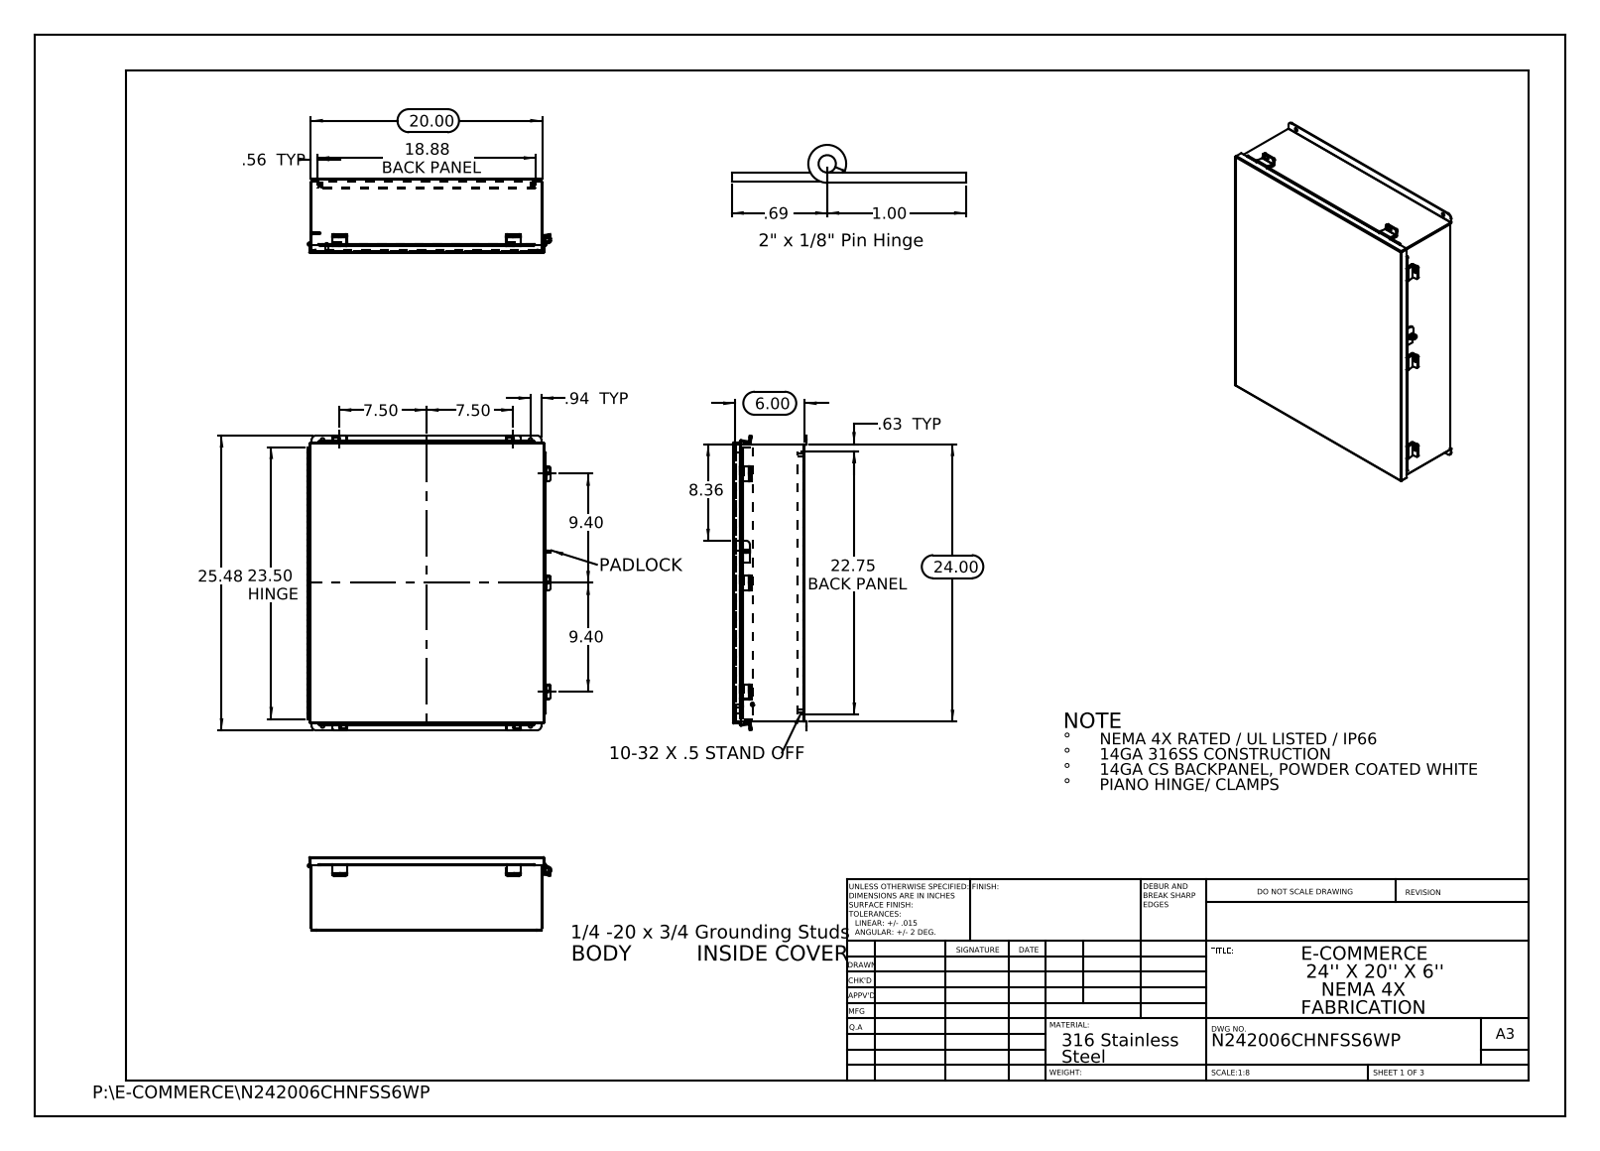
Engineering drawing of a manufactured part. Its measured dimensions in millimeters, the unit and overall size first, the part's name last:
Units: millimetres
Overall size (bounding box): 647.1 × 535.2 × 162.3
Round holes (diameter × count): ⌀6.4 ×11, ⌀4.7 ×4, ⌀7.9 ×4, ⌀3.2 ×1, ⌀3.2 ×1, ⌀9.5 ×1, ⌀9.5 ×1
Round bosses / shafts (diameter × count): ⌀8 ×4, ⌀8 ×2, ⌀6 ×2, ⌀6.9 ×1, ⌀6.4 ×1
Partial cylindrical surfaces — rounded edges, fillets, slot ends (radius × count): R3.2 ×24, R3.4 ×14, R0.3 ×13, R0.2 ×12, R2.2 ×12, R2.1 ×6, R2.5 ×6, R9.5 ×4
Main face-to-face distances: 1.9, 155.7, 153.7, 157.6, 1.9, 143, 14.6, 12.7, 141, 16.5
Hole centre spacings: 33.4, 462.8, 595, 753.1, 239.4, 381, 456.6, 466.7
Volume: 2 588 000 mm³ · Surface area: 2 761 000 mm²
Bodies: 29 solids, 1056 faces (651 planar, 385 cylindrical, 20 other)
Part name (STEP PRODUCT): N242006CHNFSS6WP JIC Clamp Bracket; N242006CHNFSS6WP JIC Cover Clamp; N242006CHNFSS6WP JIC Backpanel; N242006CHNFSS6WP JIC Top (+8 more)
STEP written by: SolidWorks 2013 (CONFIG_CONTROL_DESIGN)
